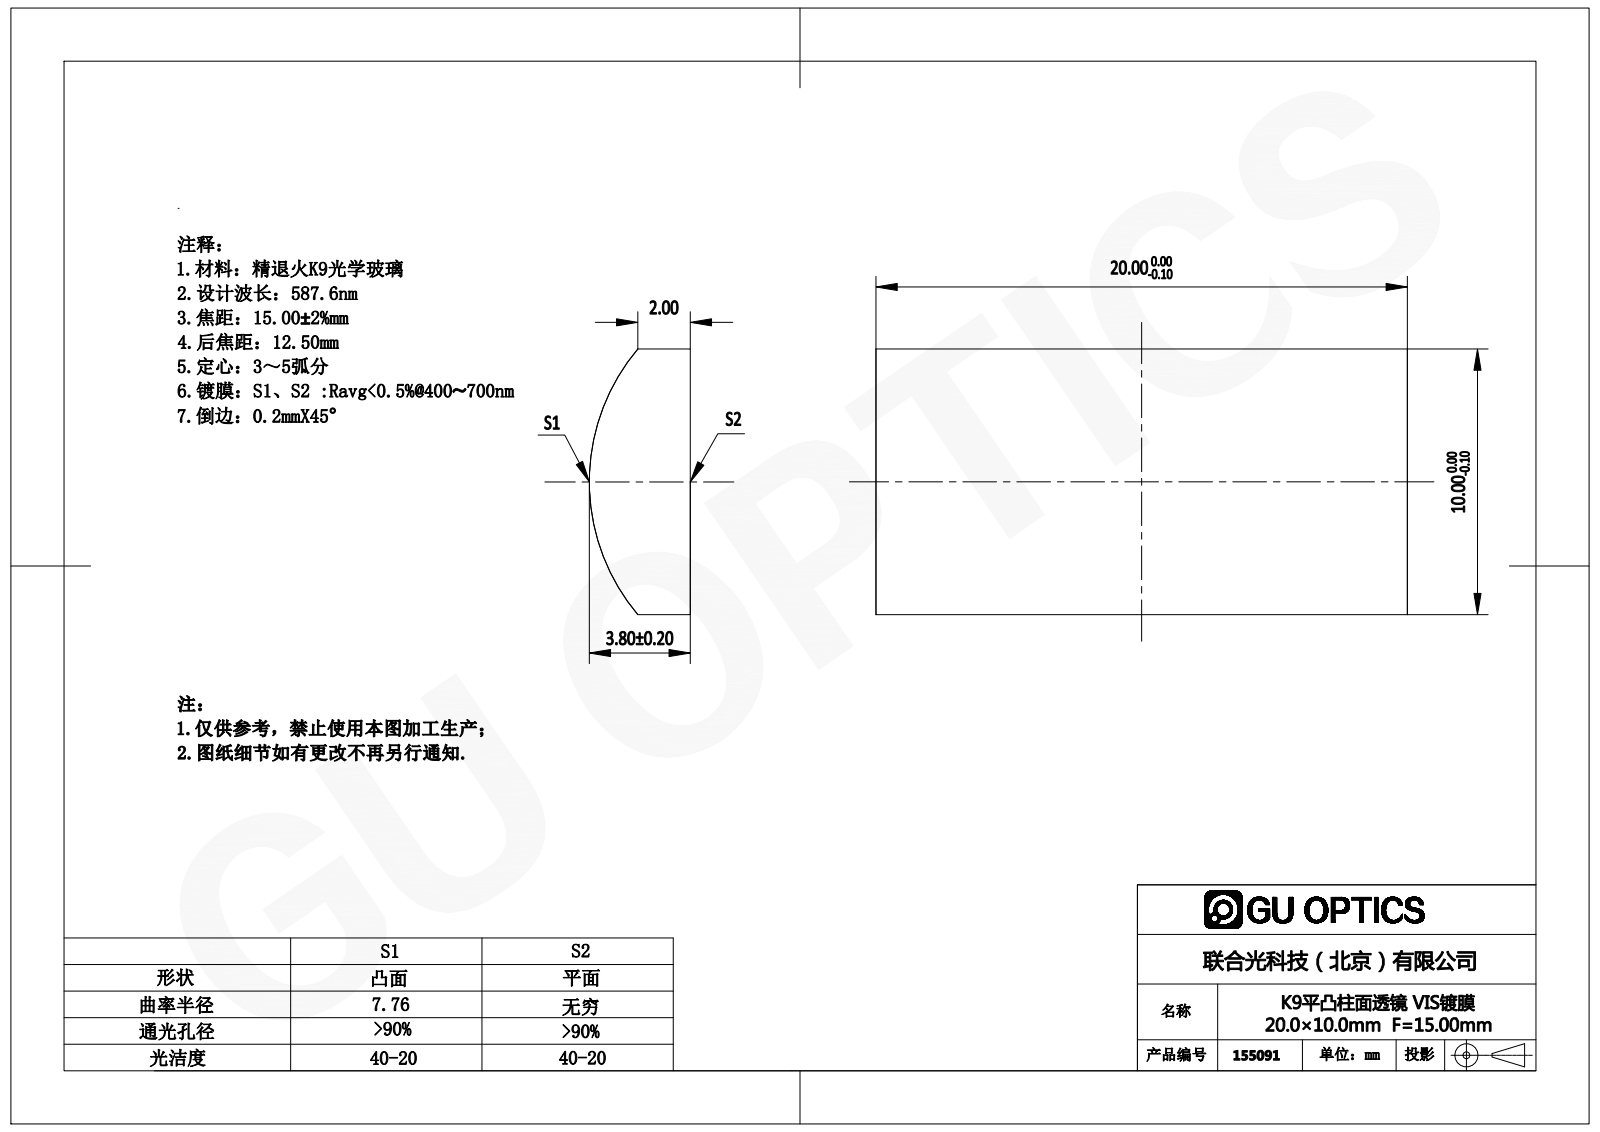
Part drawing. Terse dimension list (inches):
name: 155025
written by: SolidWorks 2016 (AUTOMOTIVE_DESIGN)
unit: in
bodies: 1 solid, 6 faces (5 planar, 1 cylindrical, 0 other)
size: 0.787 × 0.394 × 0.15
volume: 0.039 in³; area: 0.87 in²
rounds: 1× R0.306
face distances: 0.394, 0.787
